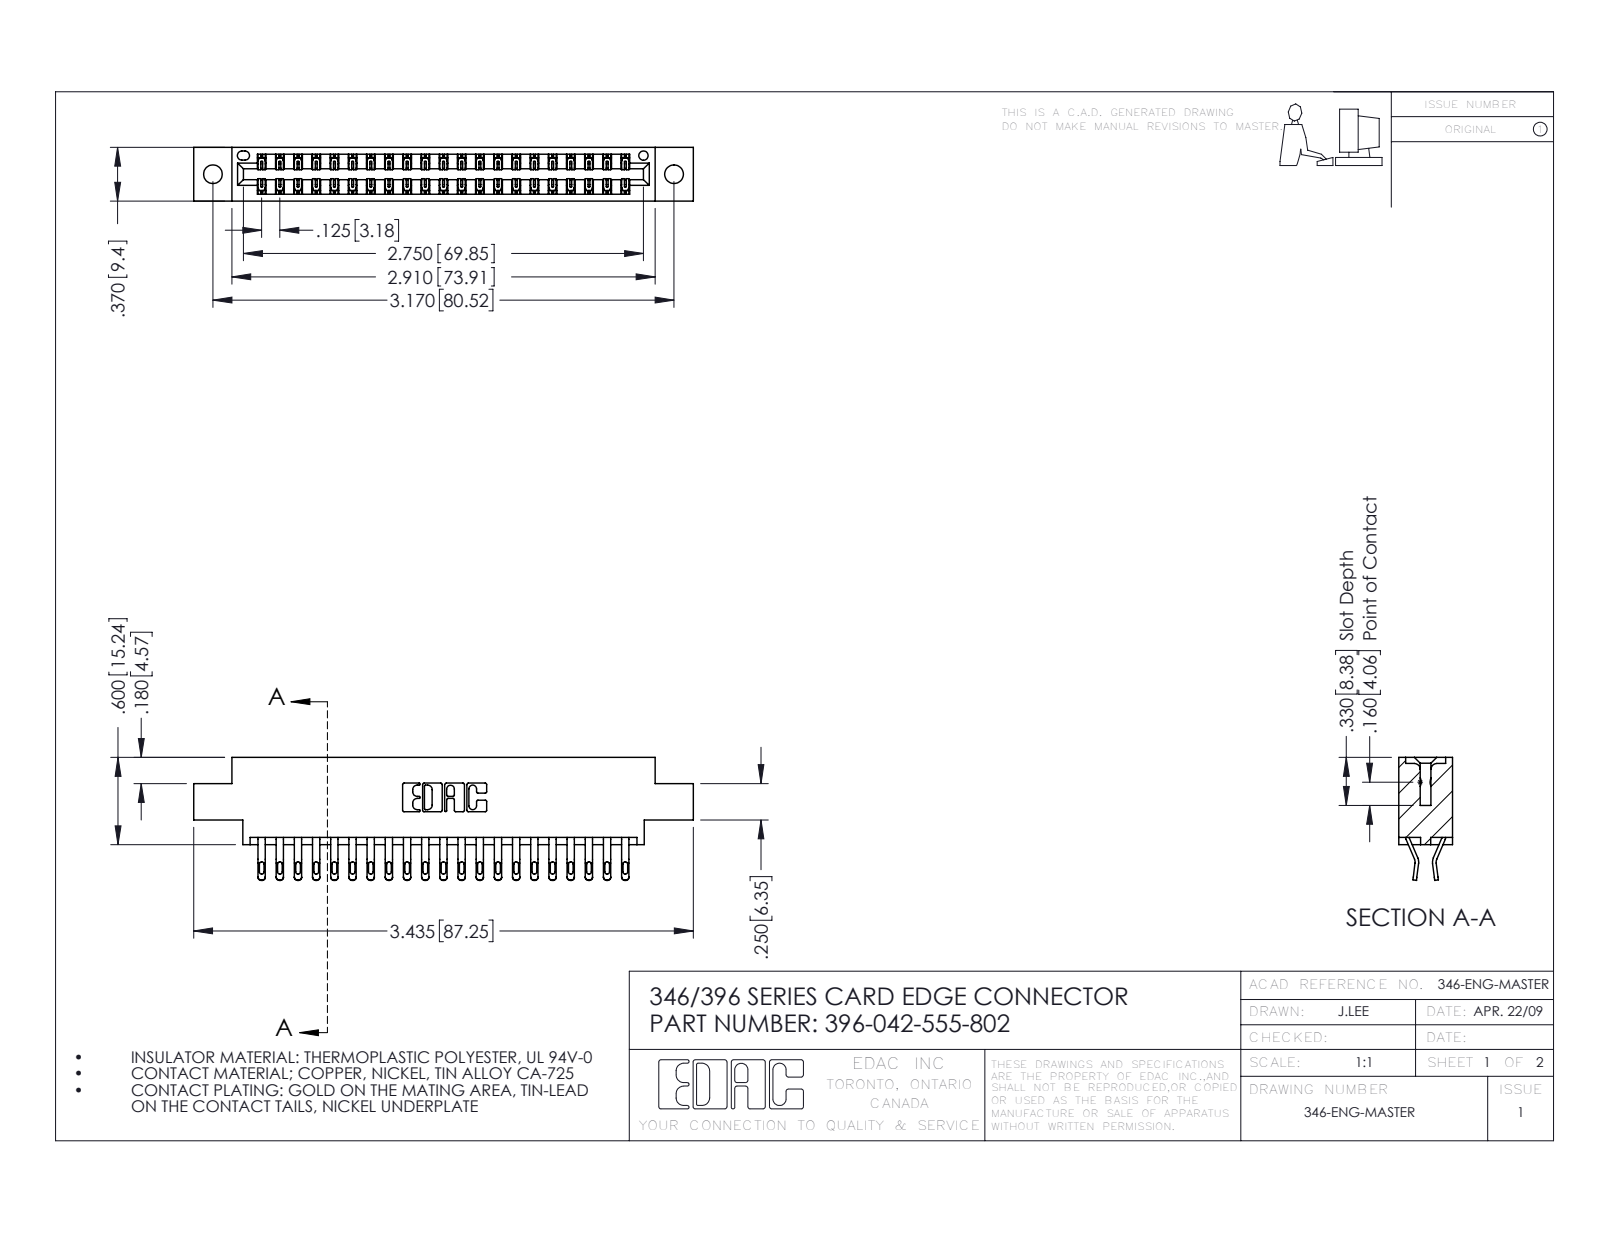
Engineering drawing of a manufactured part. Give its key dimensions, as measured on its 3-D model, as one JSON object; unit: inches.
{"part_name": "345-292-001_555 Tail; 396-042-555-802; 346 Part_0.170 Offset - 0.128 Dia", "step_written_by": "SolidWorks 2016 (CONFIG_CONTROL_DESIGN)", "units": "inches", "bodies": {"solids": 43, "faces": 2562, "planar": 1466, "cylindrical": 1096, "other": 0}, "overall_size": [3.435, 0.845, 0.37], "volume_in3": 0.505, "surface_area_in2": 17.65, "round_holes": [[0.128, 2], [0.064, 1]], "partial_cylinders_radius": [[0.016, 84], [0.02, 84], [0.006, 63], [0.01, 22], [0.007, 6], [0.031, 6], [0.026, 3], [0.01, 2]], "face_to_face_distances": [0.048, 0.322, 0.37, 0.25, 0.025, 0.072, 0.298, 0.275, 0.148, 0.222], "hole_center_spacings": [0.246, 2.963, 3.17]}
